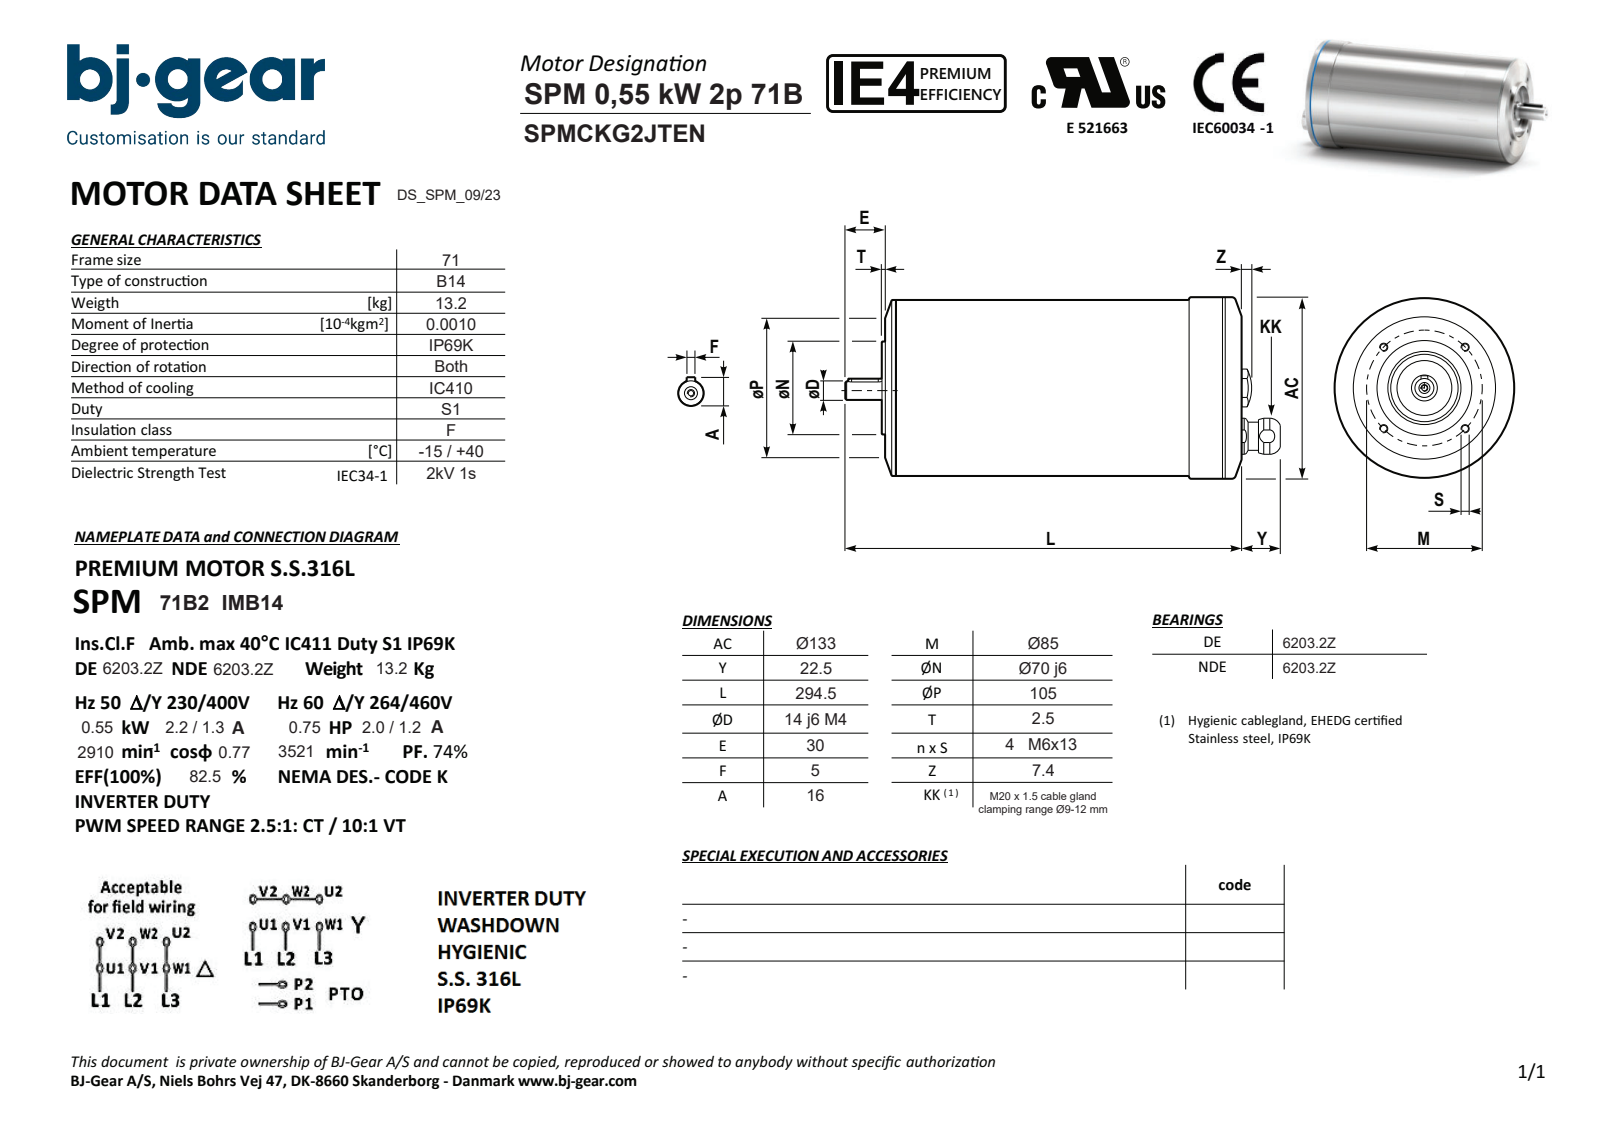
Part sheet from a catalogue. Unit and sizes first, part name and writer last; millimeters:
Units: millimetres
Overall size (bounding box): 322 × 133 × 133
Round holes (diameter × count): ⌀4.92 ×4, ⌀4.13 ×1, ⌀5.3 ×1, ⌀7 ×1, ⌀13.4 ×1, ⌀52 ×1, ⌀62 ×1
Round bosses / shafts (diameter × count): ⌀133 ×1, ⌀132.98 ×1, ⌀129 ×1, ⌀128.98 ×1, ⌀70 ×1, ⌀20 ×1, ⌀17 ×1, ⌀14 ×1
Partial cylindrical surfaces — rounded edges, fillets, slot ends (radius × count): R2.5 ×2, R12.8 ×1
Main face-to-face distances: 264.5, 259, 5.5, 263.5, 4.5, 1, 2.5, 8, 267, 3.5
Hole centre spacings: 42.5, 60.1, 30.31, 70.75, 84.99, 34
Volume: 3 471 000 mm³ · Surface area: 138 275 mm²
Bodies: 1 solid, 90 faces (31 planar, 33 cylindrical, 26 other)
Part name (STEP PRODUCT): SPMCKG2JTENN4KSA1-N---NNN
STEP written by: Solid Edge (AUTOMOTIVE_DESIGN)
